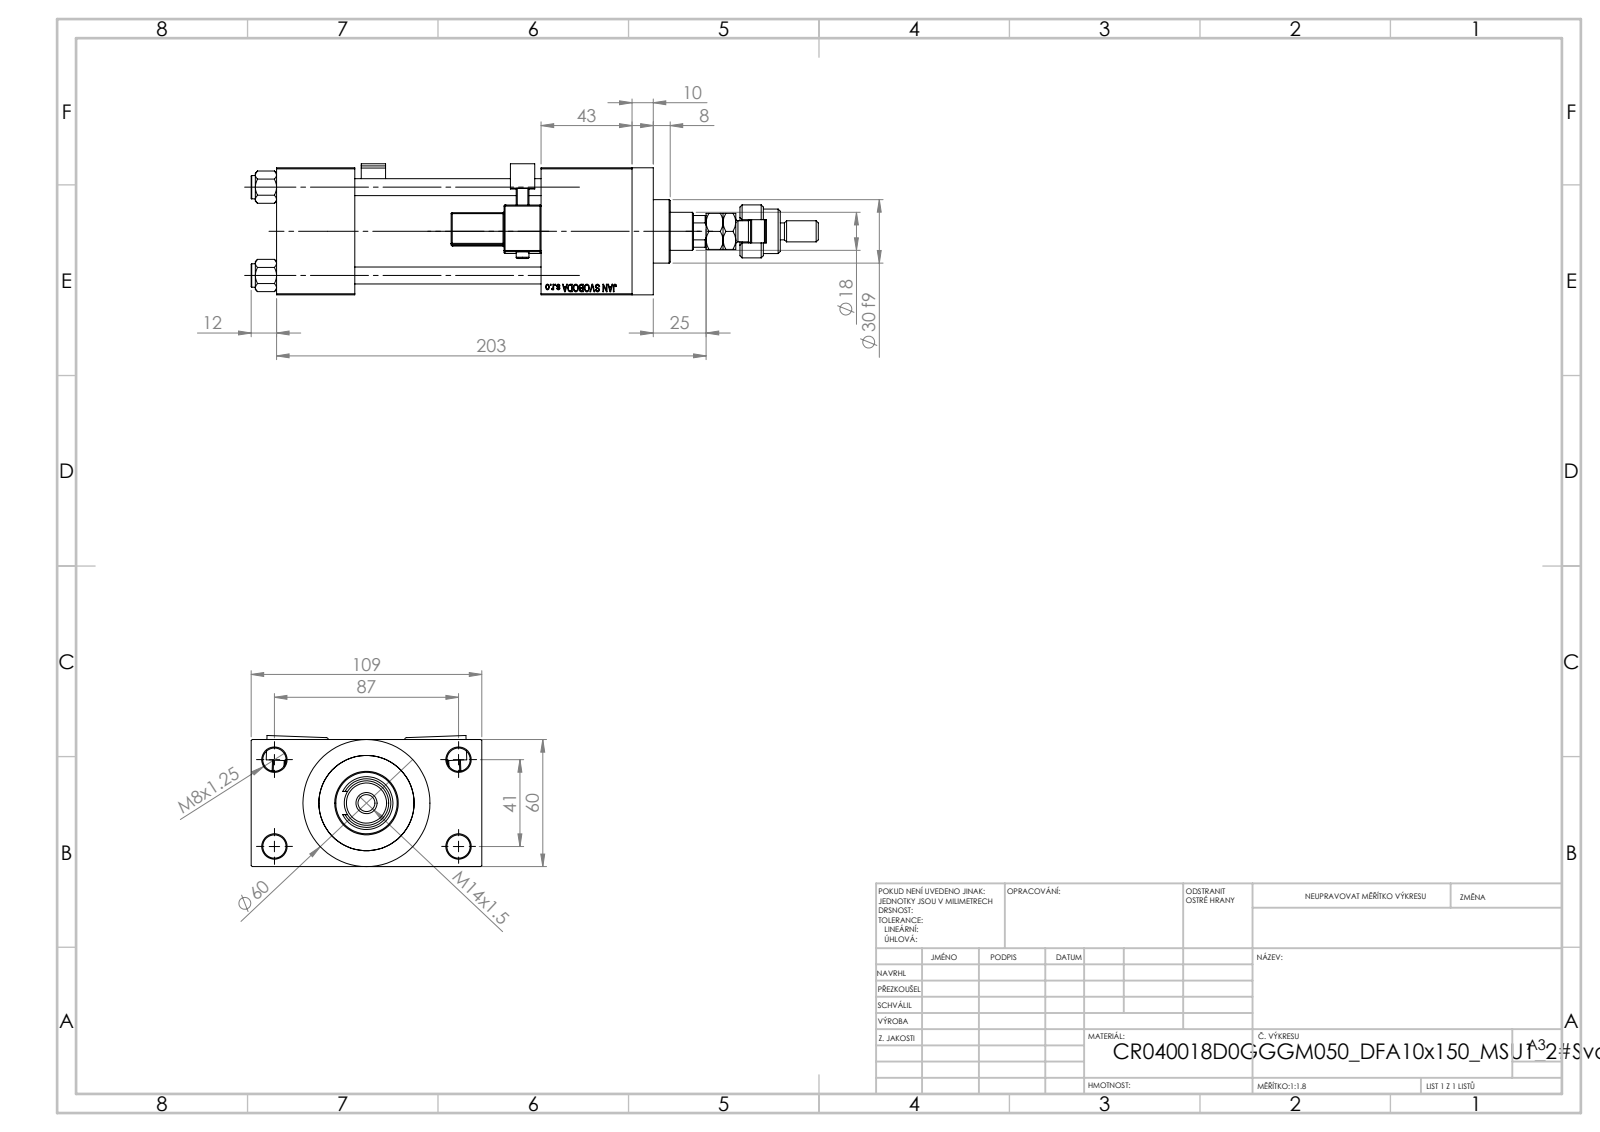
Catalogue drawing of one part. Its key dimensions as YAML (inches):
part_name: "V215CR_VCP_D; FEMALE_PART_FOR_DFA; V215CR_MSU; V215_VC_A (+4 more)"
step_written_by: "SolidWorks 2019 (CONFIG_CONTROL_DESIGN)"
units: inches
bodies: {solids: 15, faces: 1344, planar: 584, cylindrical: 162, other: 598}
overall_size: [10.551, 4.291, 2.437]
volume: 36.38
surface_area: 235
round_holes:
  - {diameter: 0.315, count: 4}
  - {diameter: 0.433, count: 4}
  - {diameter: 0.276, count: 2}
  - {diameter: 0.656, count: 2}
  - {diameter: 0.945, count: 2}
  - {diameter: 0.335, count: 1}
  - {diameter: 0.709, count: 1}
  - {diameter: 0.827, count: 1}
  - {diameter: 1.22, count: 1}
  - {diameter: 1.575, count: 1}
  - {diameter: 1.772, count: 1}
round_bosses_or_shafts:
  - {diameter: 0.433, count: 4}
  - {diameter: 0.236, count: 2}
  - {diameter: 2.362, count: 1}
  - {diameter: 1.811, count: 1}
  - {diameter: 1.181, count: 1}
  - {diameter: 0.984, count: 1}
  - {diameter: 0.63, count: 1}
  - {diameter: 0.394, count: 1}
partial_cylinders:
  - {radius: 0.02, count: 48}
  - {radius: 0.039, count: 2}
  - {radius: 0.098, count: 2}
  - {radius: 0.157, count: 2}
  - {radius: 0.217, count: 1}
  - {radius: 0.335, count: 1}
  - {radius: 0.344, count: 1}
face_to_face_distances: [2.362, 3.465, 0.965, 3.327, 1.457, 4.921, 6.614, 5.157, 1.693, 4.291]
hole_center_spacings: [0.892, 1.161, 1.642, 1.856, 1.893, 2.533, 3.011, 1.614]
